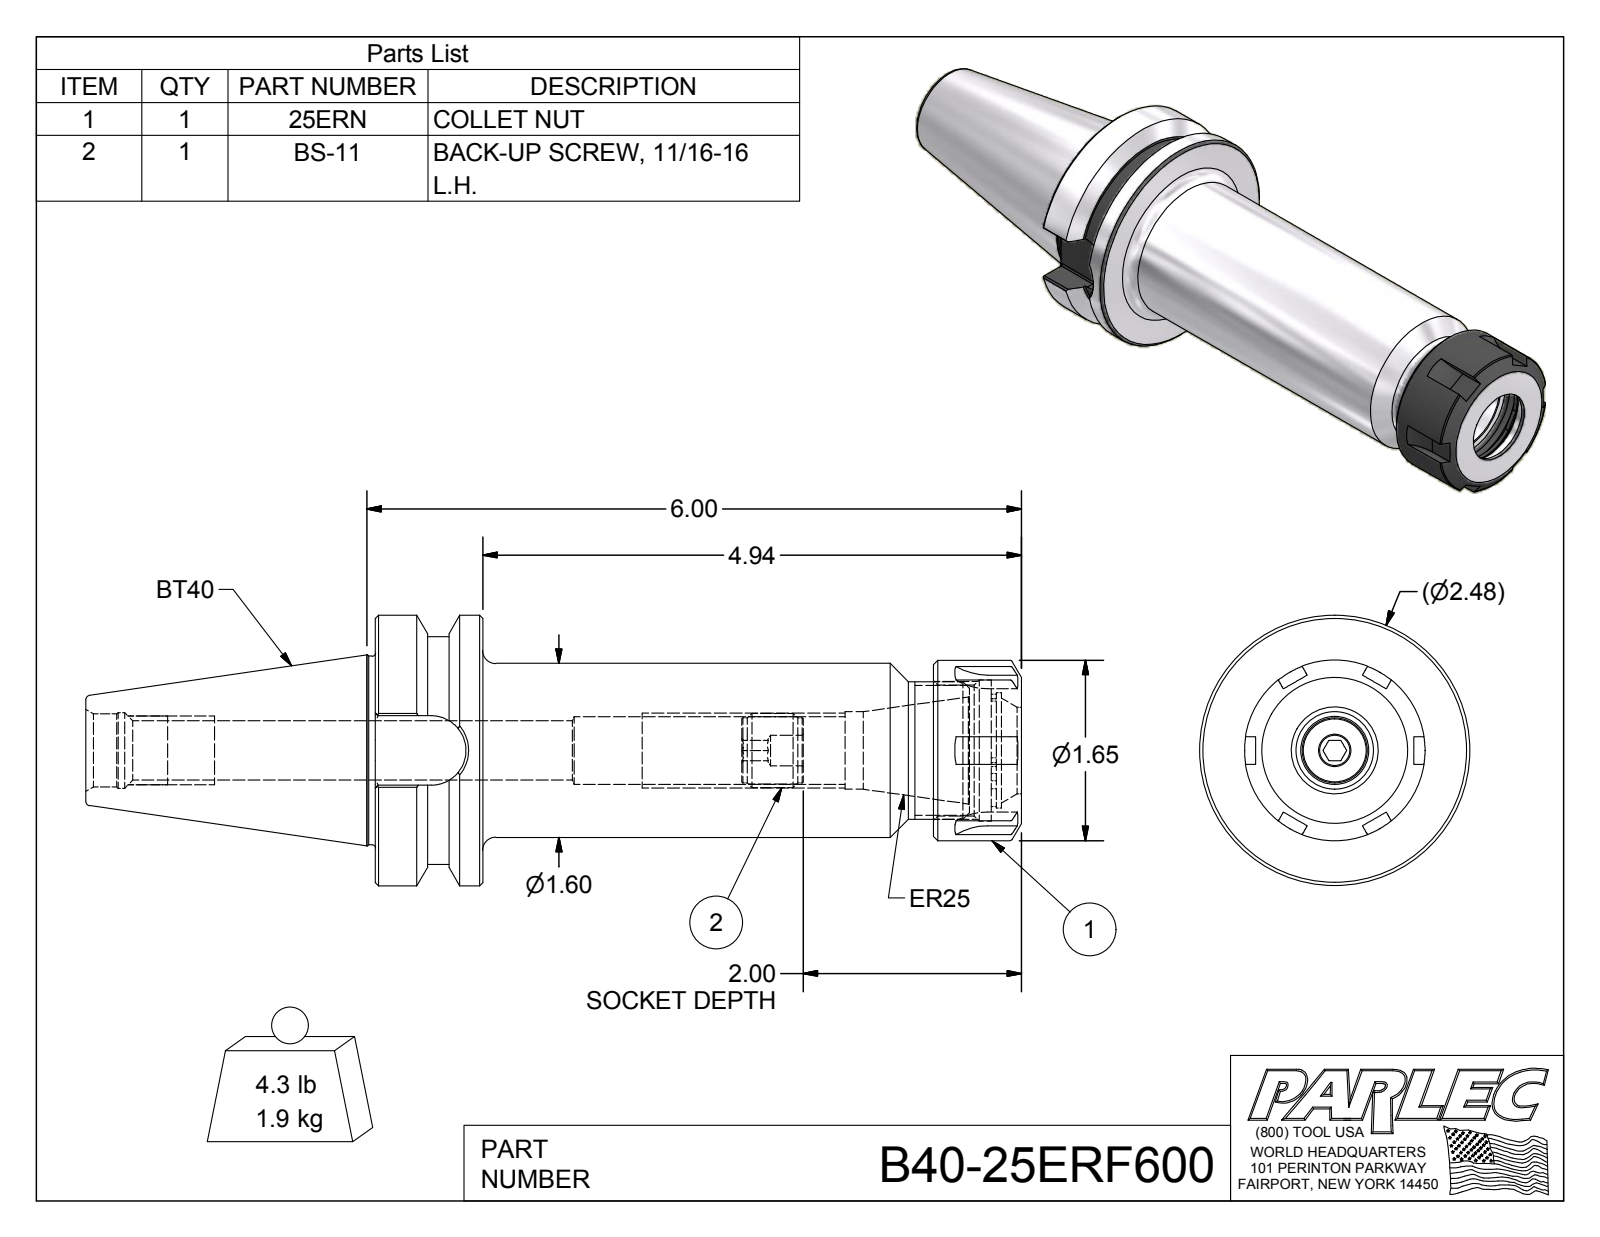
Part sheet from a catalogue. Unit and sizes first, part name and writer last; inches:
Units: inches
Overall size (bounding box): 8.575 × 2.48 × 2.48
Round holes (diameter × count): ⌀0.28 ×1, ⌀0.545 ×1, ⌀0.62 ×1, ⌀0.67 ×1, ⌀0.694 ×1, ⌀0.71 ×1, ⌀0.794 ×1, ⌀1.057 ×1, ⌀1.201 ×1, ⌀1.294 ×1
Round bosses / shafts (diameter × count): ⌀2.48 ×1, ⌀2.087 ×1, ⌀1.73 ×1, ⌀1.654 ×1, ⌀1.595 ×1, ⌀1.26 ×1, ⌀0.681 ×1, ⌀0.595 ×1
Partial cylindrical surfaces — rounded edges, fillets, slot ends (radius × count): R0.02 ×8, R0.5 ×6, R0.319 ×1, R0.472 ×1, R0.515 ×1
Main face-to-face distances: 0.984, 5.922, 4.938, 5.115, 4.131, 0.807, 5.646, 4.663, 0.531, 0.276
Volume: 15.14 in³ · Surface area: 76.81 in²
Bodies: 3 solids, 145 faces (60 planar, 43 cylindrical, 42 other)
Part name (STEP PRODUCT): B40-25ERF600; B40-25ER6-1; 25ERN; BS-11
STEP written by: Autodesk Inventor 2012 (AUTOMOTIVE_DESIGN)
